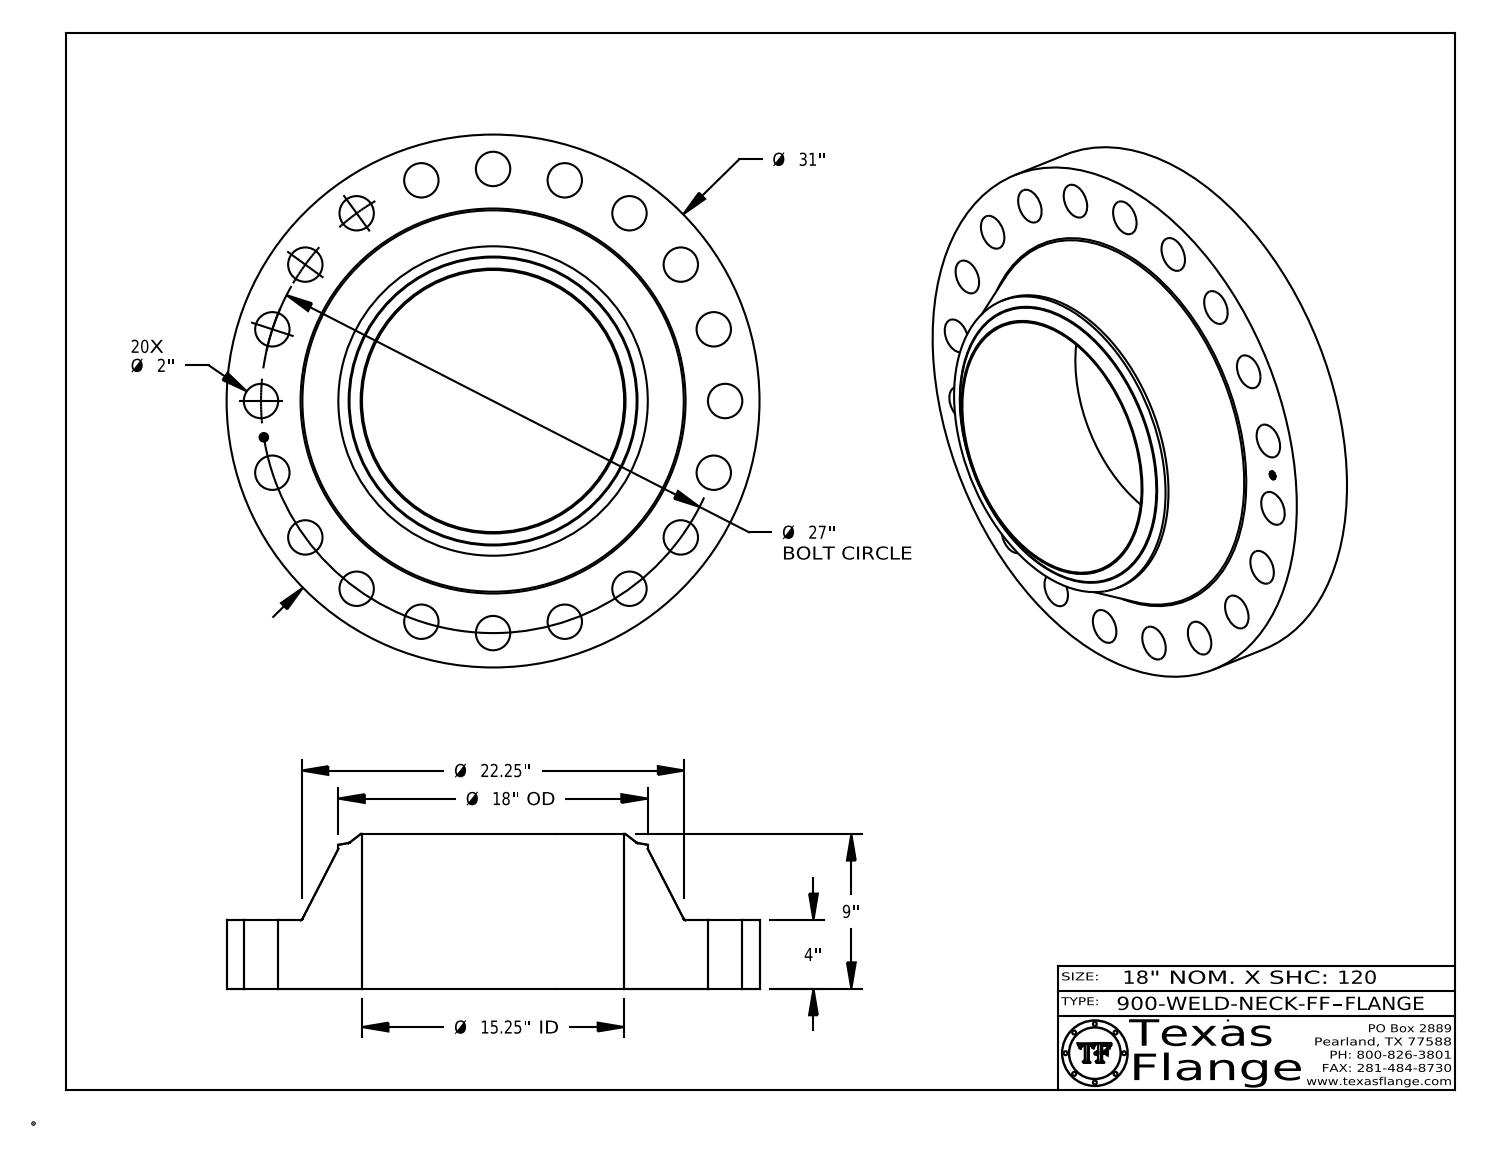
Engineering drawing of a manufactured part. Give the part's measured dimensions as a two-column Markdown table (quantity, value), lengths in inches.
| quantity | value |
| --- | --- |
| part name | 900-WELD-NECK-FF |
| STEP written by | CATIA V5 STEP AP214 (AUTOMOTIVE_DESIGN) |
| units | inches |
| bodies | 1 solid, 444 faces (368 planar, 66 cylindrical, 10 other) |
| overall size | 31 × 31 × 9 |
| volume | 2 636 in³ |
| surface area | 2 523 in² |
| round holes (diameter × count) | 2 × 20, 0.495 × 1, 15.25 × 1 |
| round bosses / shafts (diameter × count) | 0.03 × 8, 31 × 1, 18 × 1, 0.39 × 1 |
| main face-to-face distances | 4, 9, 5, 3.985, 0.015, 5.015, 0.148, 0.145, 0.027, 0.096 |
| hole center spacings | 13.5, 21.843, 24.057, 25.678, 26.668, 4.224, 8.343, 12.258 |
